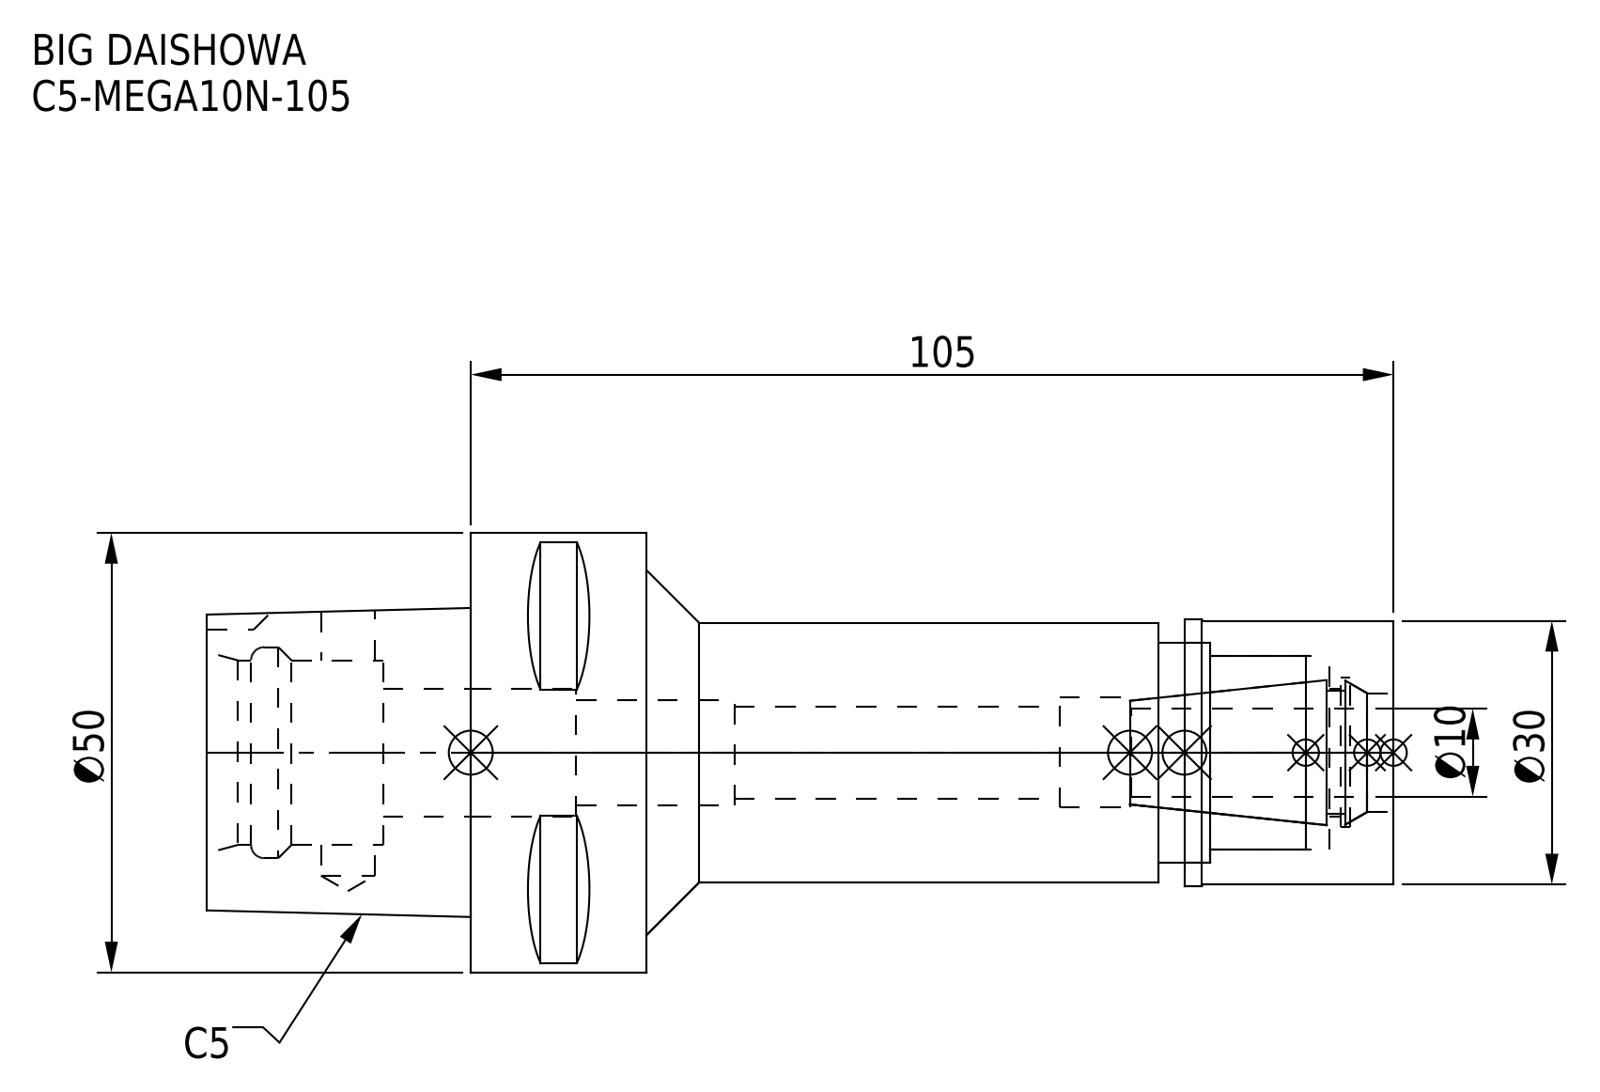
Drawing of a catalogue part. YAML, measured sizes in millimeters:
part_name: "C5-MEGA10N-105-100.stp; DXF_TEMP_ASSY_ASM_4_ASM.stp; C5-MEGA10N-105; C5-MEGA10N-105-100-FreeParts (+3 more)"
step_written_by: "SolidWorks 2019 (CONFIG_CONTROL_DESIGN)"
units: millimeters
bodies: {solids: 2, faces: 98, planar: 39, cylindrical: 41, other: 18}
overall_size: [135, 50, 50]
volume: 103038
surface_area: 27125
round_holes:
  - {diameter: 6.1, count: 1}
  - {diameter: 10.4, count: 1}
  - {diameter: 12, count: 1}
  - {diameter: 12.5, count: 1}
  - {diameter: 13.5, count: 1}
  - {diameter: 14.5, count: 1}
  - {diameter: 17, count: 1}
  - {diameter: 21, count: 1}
  - {diameter: 22, count: 1}
  - {diameter: 24, count: 1}
  - {diameter: 25, count: 1}
round_bosses_or_shafts:
  - {diameter: 50, count: 1}
  - {diameter: 30.3, count: 1}
  - {diameter: 30, count: 1}
  - {diameter: 29.5, count: 1}
partial_cylinders:
  - {radius: 4, count: 1}
face_to_face_distances: [20, 105, 30, 85, 10, 135, 50, 23.8, 61.2, 81.2]
